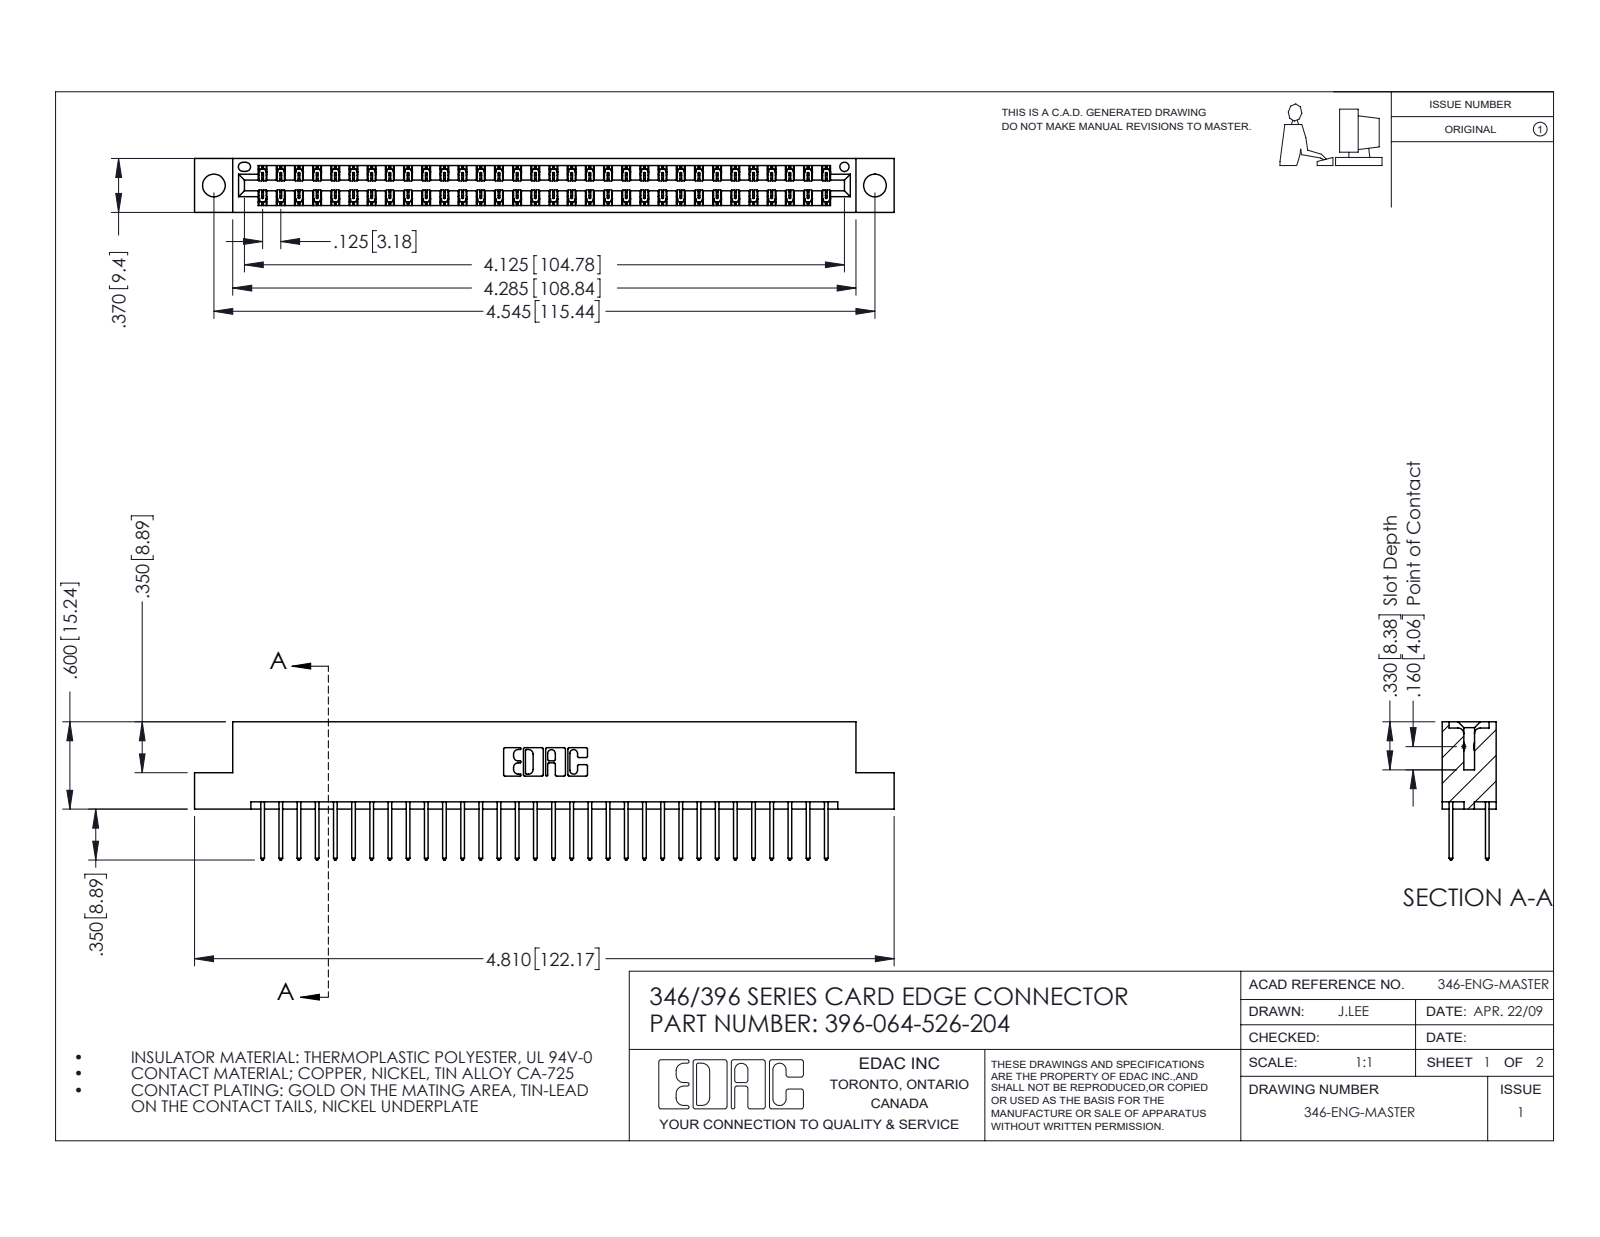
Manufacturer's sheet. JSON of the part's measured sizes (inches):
{"part_name": "345-292-001_345-293-126; 346 Part_Flush Mounting Lugs - 0.156 Dia-TH; 396-064-526-204", "step_written_by": "SolidWorks 2016 (CONFIG_CONTROL_DESIGN)", "units": "inches", "bodies": {"solids": 65, "faces": 3450, "planar": 2316, "cylindrical": 1134, "other": 0}, "overall_size": [4.81, 0.95, 0.37], "volume_in3": 0.723, "surface_area_in2": 25.45, "round_holes": [[0.156, 2], [0.064, 1]], "partial_cylinders_radius": [[0.006, 96], [0.01, 64], [0.01, 22], [0.007, 6], [0.031, 6], [0.026, 3], [0.014, 2], [0.022, 2]], "face_to_face_distances": [0.048, 0.322, 0.25, 0.37, 0.072, 0.298, 0.025, 0.275, 0.148, 0.222], "hole_center_spacings": [0.246, 4.337, 4.545]}
